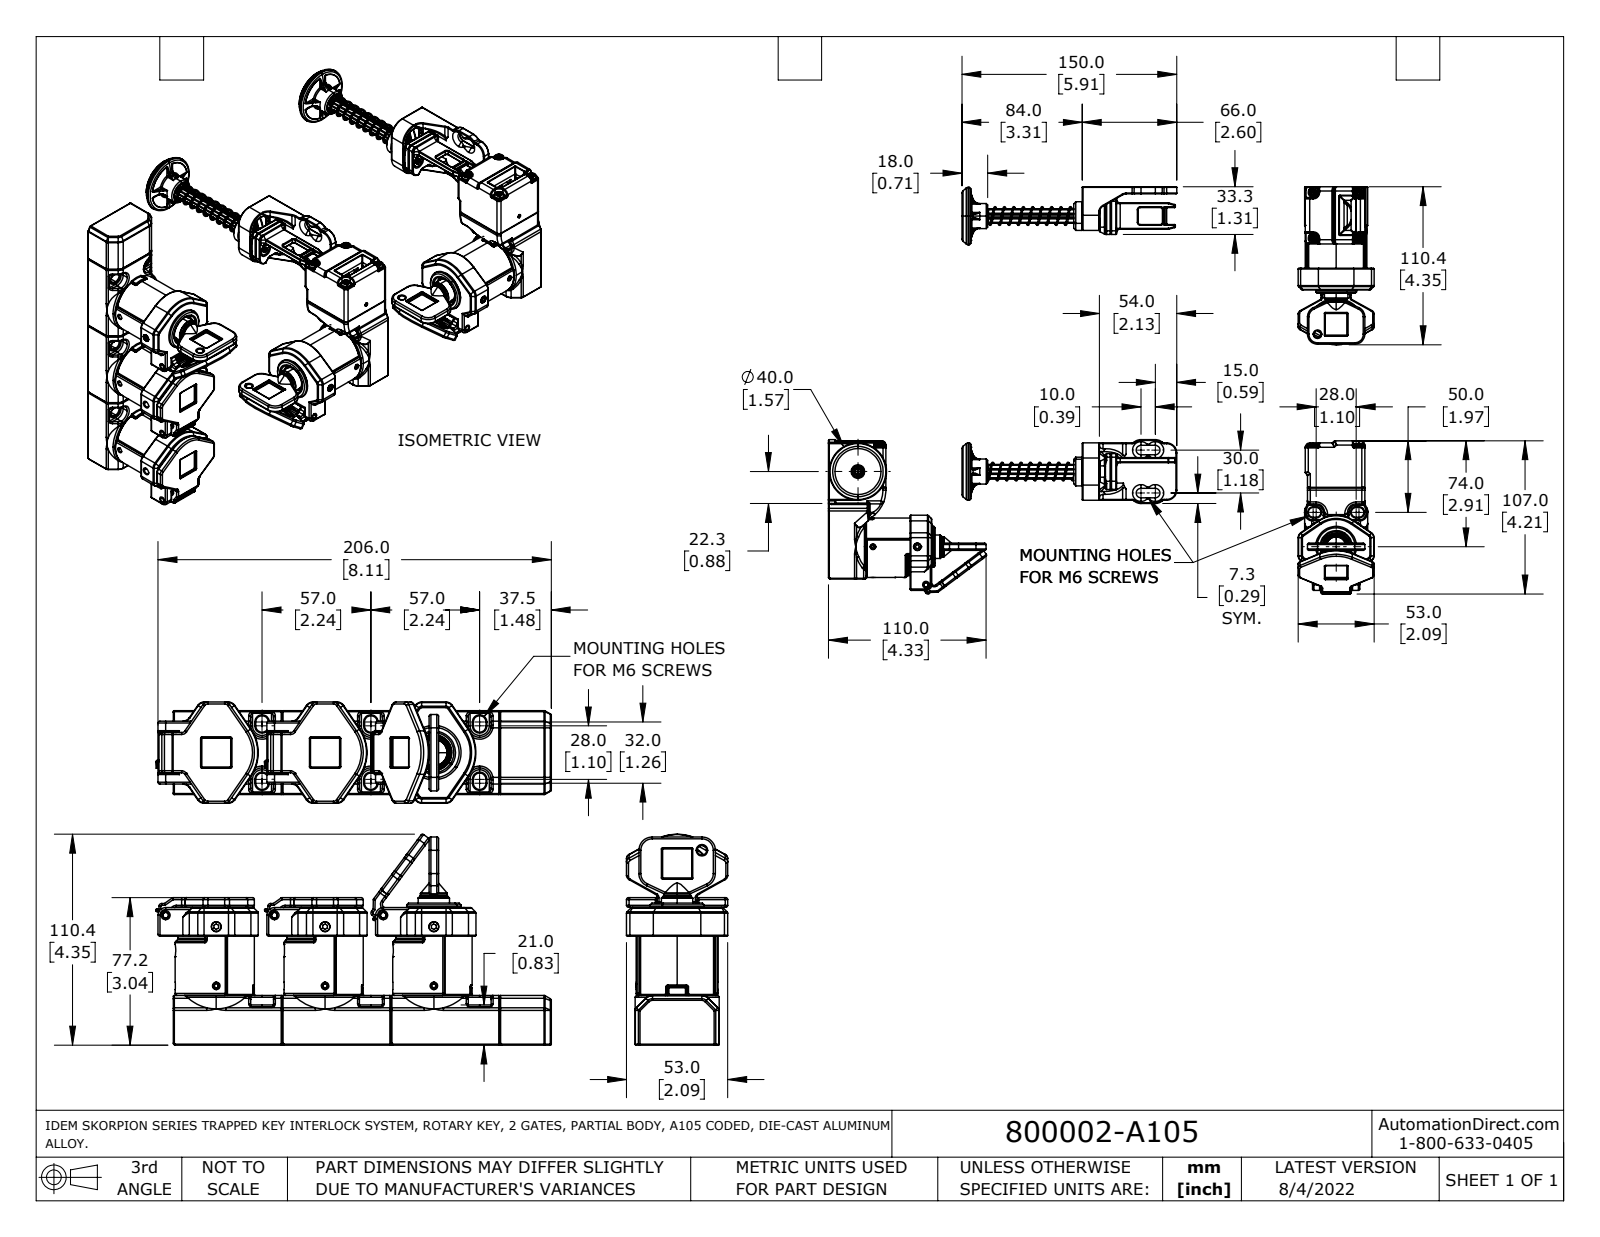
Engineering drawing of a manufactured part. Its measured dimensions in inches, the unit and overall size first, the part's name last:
Units: inches
Overall size (bounding box): 10.528 × 9.024 × 8.227
Round holes (diameter × count): ⌀0.177 ×12, ⌀0.13 ×11, ⌀0.165 ×8, ⌀0.138 ×7, ⌀0.315 ×6, ⌀0.157 ×4, ⌀0.197 ×4, ⌀1.606 ×4, ⌀0.087 ×2, ⌀0.098 ×2, ⌀0.12 ×2, ⌀0.236 ×2
Round bosses / shafts (diameter × count): ⌀0.051 ×14, ⌀0.291 ×8, ⌀0.138 ×7, ⌀0.154 ×6, ⌀1.575 ×4, ⌀0.276 ×4, ⌀0.122 ×4, ⌀0.394 ×3
Partial cylindrical surfaces — rounded edges, fillets, slot ends (radius × count): R0.02 ×809, R0.039 ×409, R0.012 ×76, R0.079 ×63, R0.157 ×39, R0.118 ×24, R0.059 ×22, R0.031 ×18
Main face-to-face distances: 0.118, 1.732, 0.197, 7.115, 8.847, 3.039, 1.575, 2.244, 0.039, 3
Hole centre spacings: 2.244, 4.488, 0.822, 1.724, 2.5, 0.891, 1.07, 1.102
Volume: 37.06 in³ · Surface area: 306.4 in²
Bodies: 7 solids, 5898 faces (1344 planar, 2439 cylindrical, 2115 other)
Part name (STEP PRODUCT): 800002-A103_3; 800002-A103_1; 800002-A103; 800002-A103_2
STEP written by: SolidWorks 2021 (AUTOMOTIVE_DESIGN)
